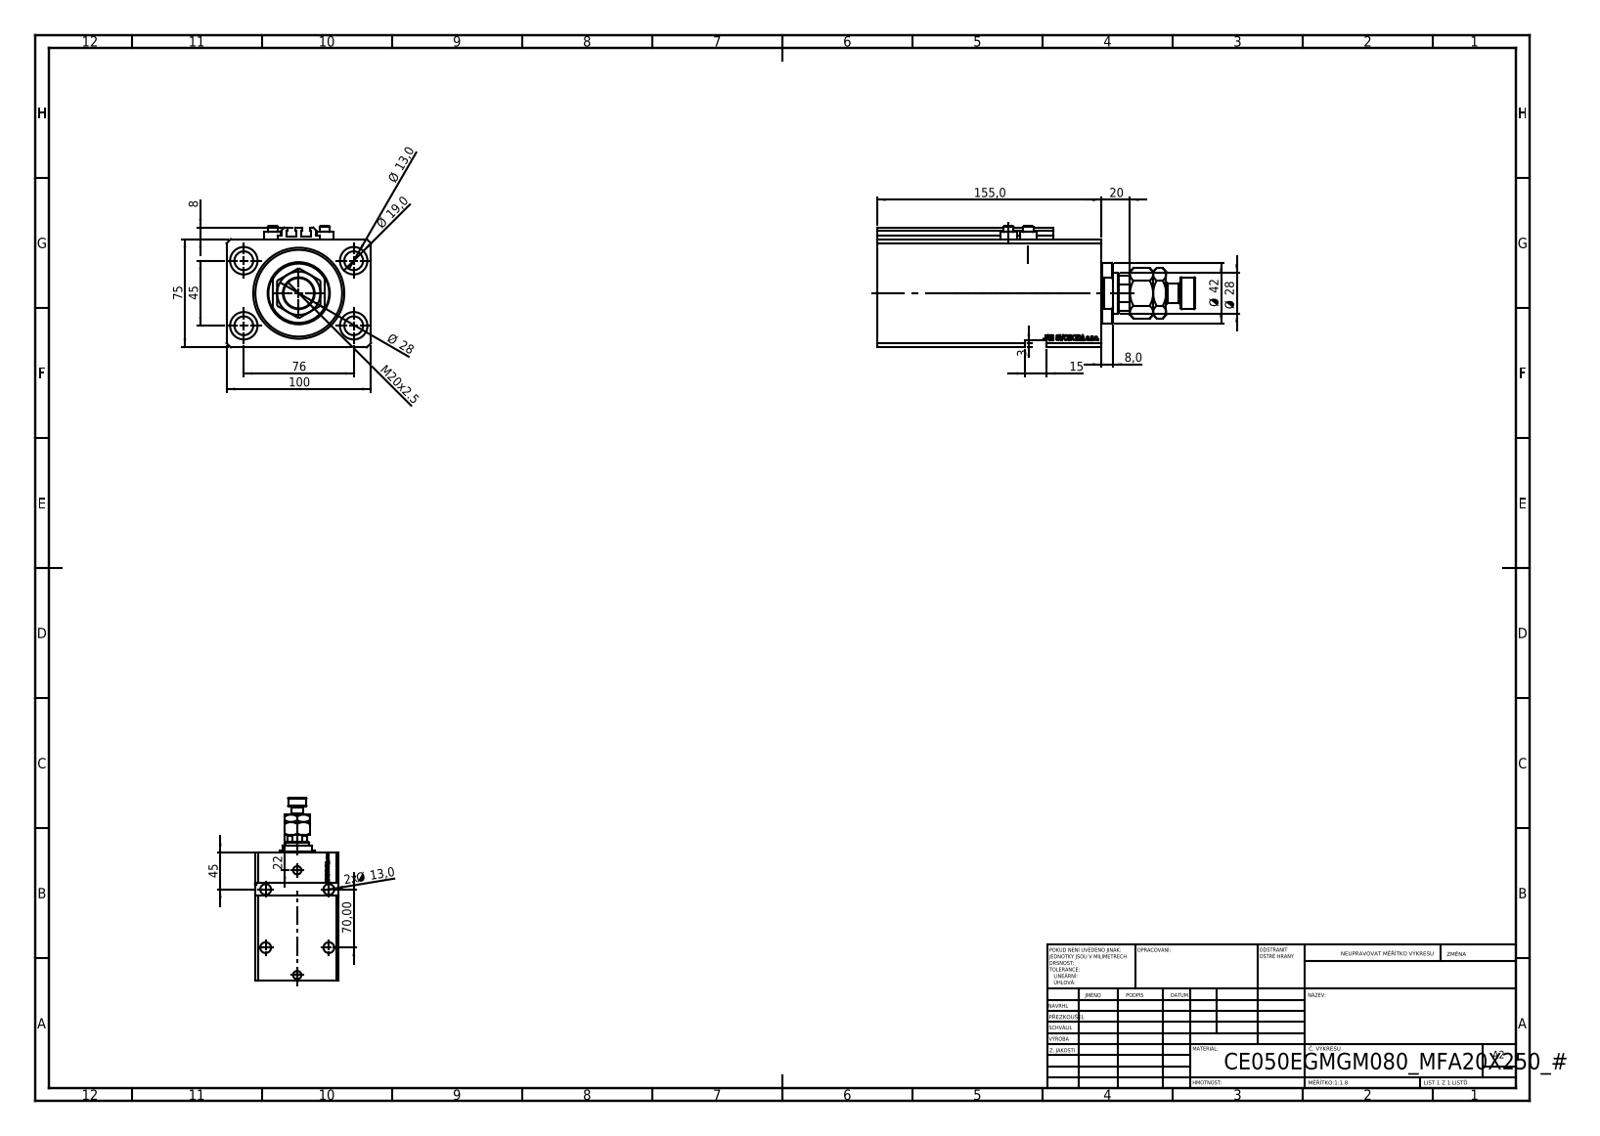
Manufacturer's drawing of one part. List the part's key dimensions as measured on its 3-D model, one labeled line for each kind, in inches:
Part name (STEP PRODUCT): V250CE_VC_E; MFA; V250CE_C_VCP; ALLEN BOLT V250CE (+1 more)
STEP written by: SolidWorks 2019 (CONFIG_CONTROL_DESIGN)
Units: inches
Bodies: 9 solids, 1160 faces (551 planar, 150 cylindrical, 459 other)
Overall size (bounding box): 8.661 × 3.937 × 3.307
Volume: 58.91 in³ · Surface area: 281.3 in²
Round holes (diameter × count): ⌀0.512 ×8, ⌀0.049 ×4, ⌀0.157 ×4, ⌀0.748 ×4, ⌀0.394 ×2, ⌀0.518 ×2, ⌀0.787 ×2, ⌀0.728 ×1, ⌀1.102 ×1, ⌀1.969 ×1, ⌀2.48 ×1
Round bosses / shafts (diameter × count): ⌀0.457 ×4, ⌀0.276 ×4, ⌀1.654 ×1, ⌀0.866 ×1, ⌀0.551 ×1
Partial cylindrical surfaces — rounded edges, fillets, slot ends (radius × count): R0.008 ×10, R0.531 ×1
Main face-to-face distances: 2.953, 3.937, 0.787, 6.102, 0.469, 5.634, 5.315, 4.846, 0.118, 0.315
Hole centre spacings: 1.739, 2.992, 0.535, 0.816, 1.086, 1.324, 1.417, 1.515
